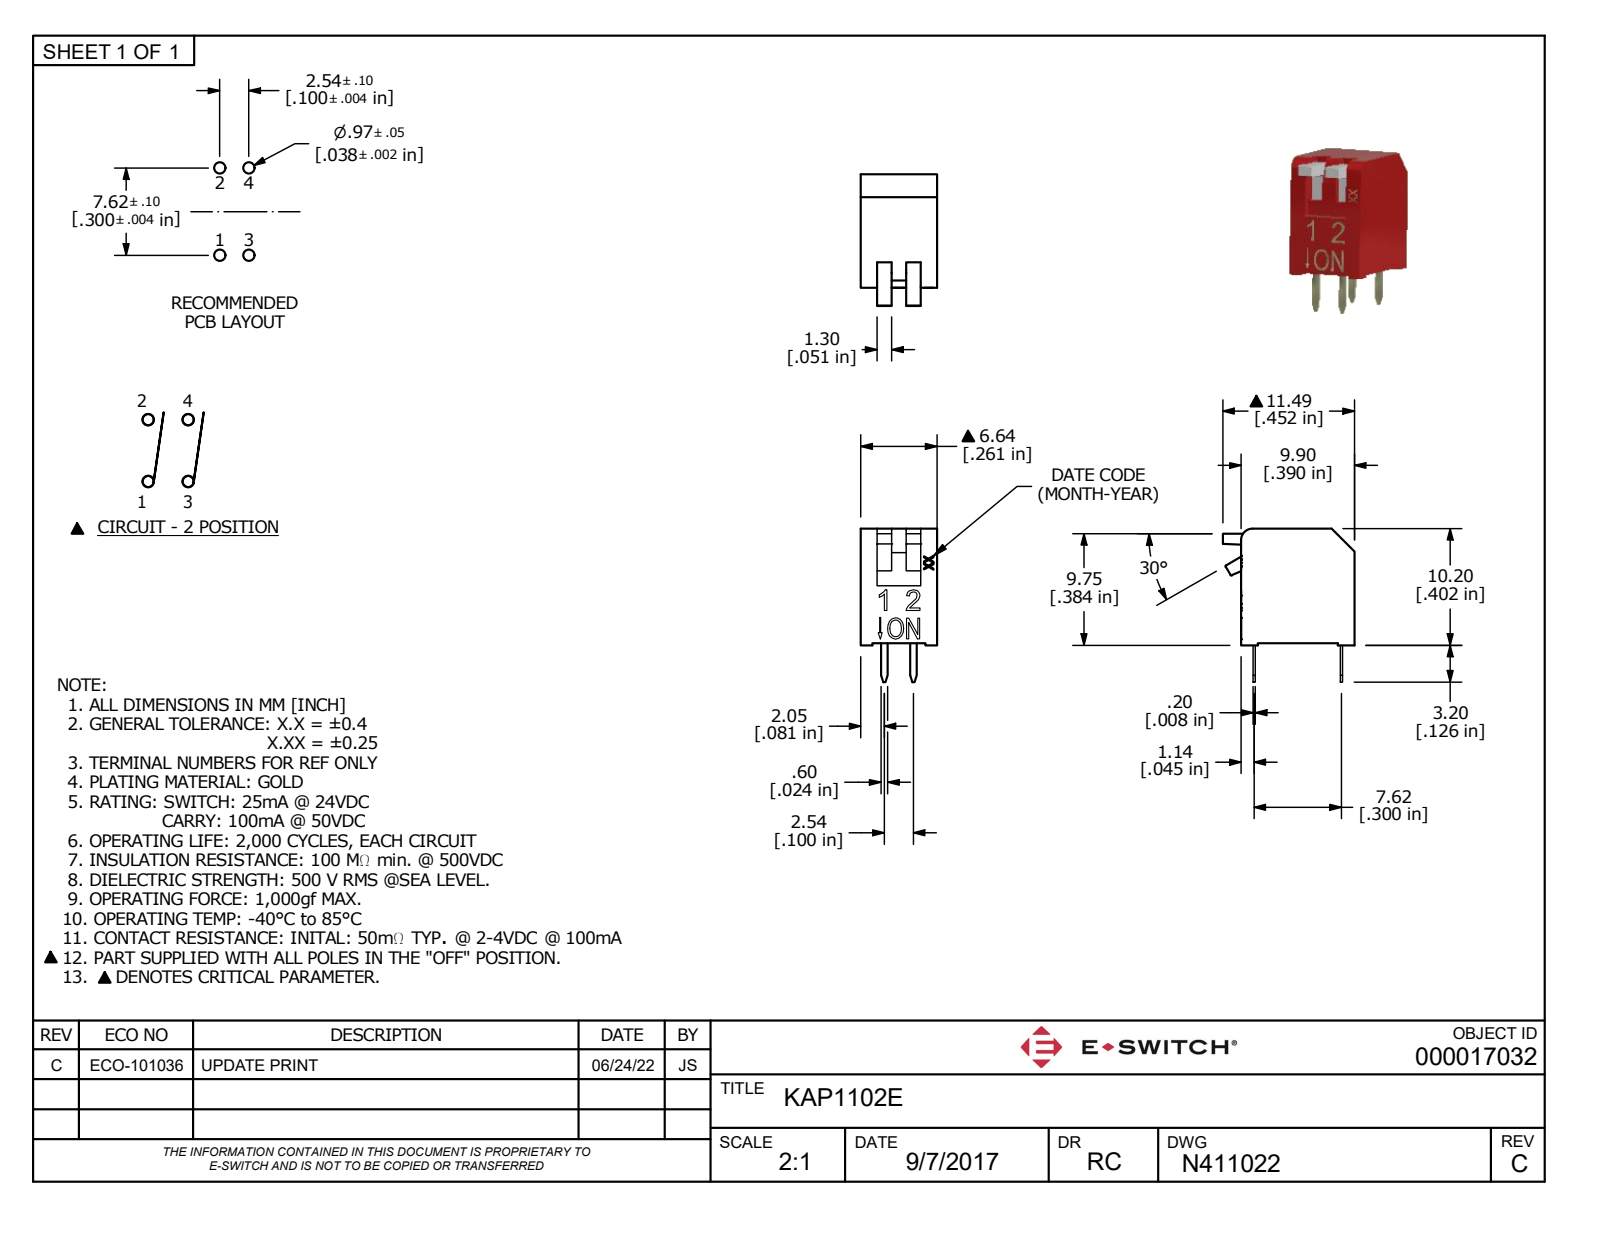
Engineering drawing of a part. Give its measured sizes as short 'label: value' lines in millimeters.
name: 000017032_Shrinkwrap_1
written by: Autodesk Inventor 2020 (AUTOMOTIVE_DESIGN)
unit: mm
bodies: 1 solid, 177 faces (132 planar, 15 cylindrical, 30 other)
size: 13.4 × 11.5 × 6.6
volume: 640 mm³; area: 509 mm²
rounds: 2× R0.3, 1× R0.3, 1× R1
face distances: 6.6, 10, 9.9, 1.4, 5.2, 1.2, 2.5, 9.6, 0.5, 2.7
